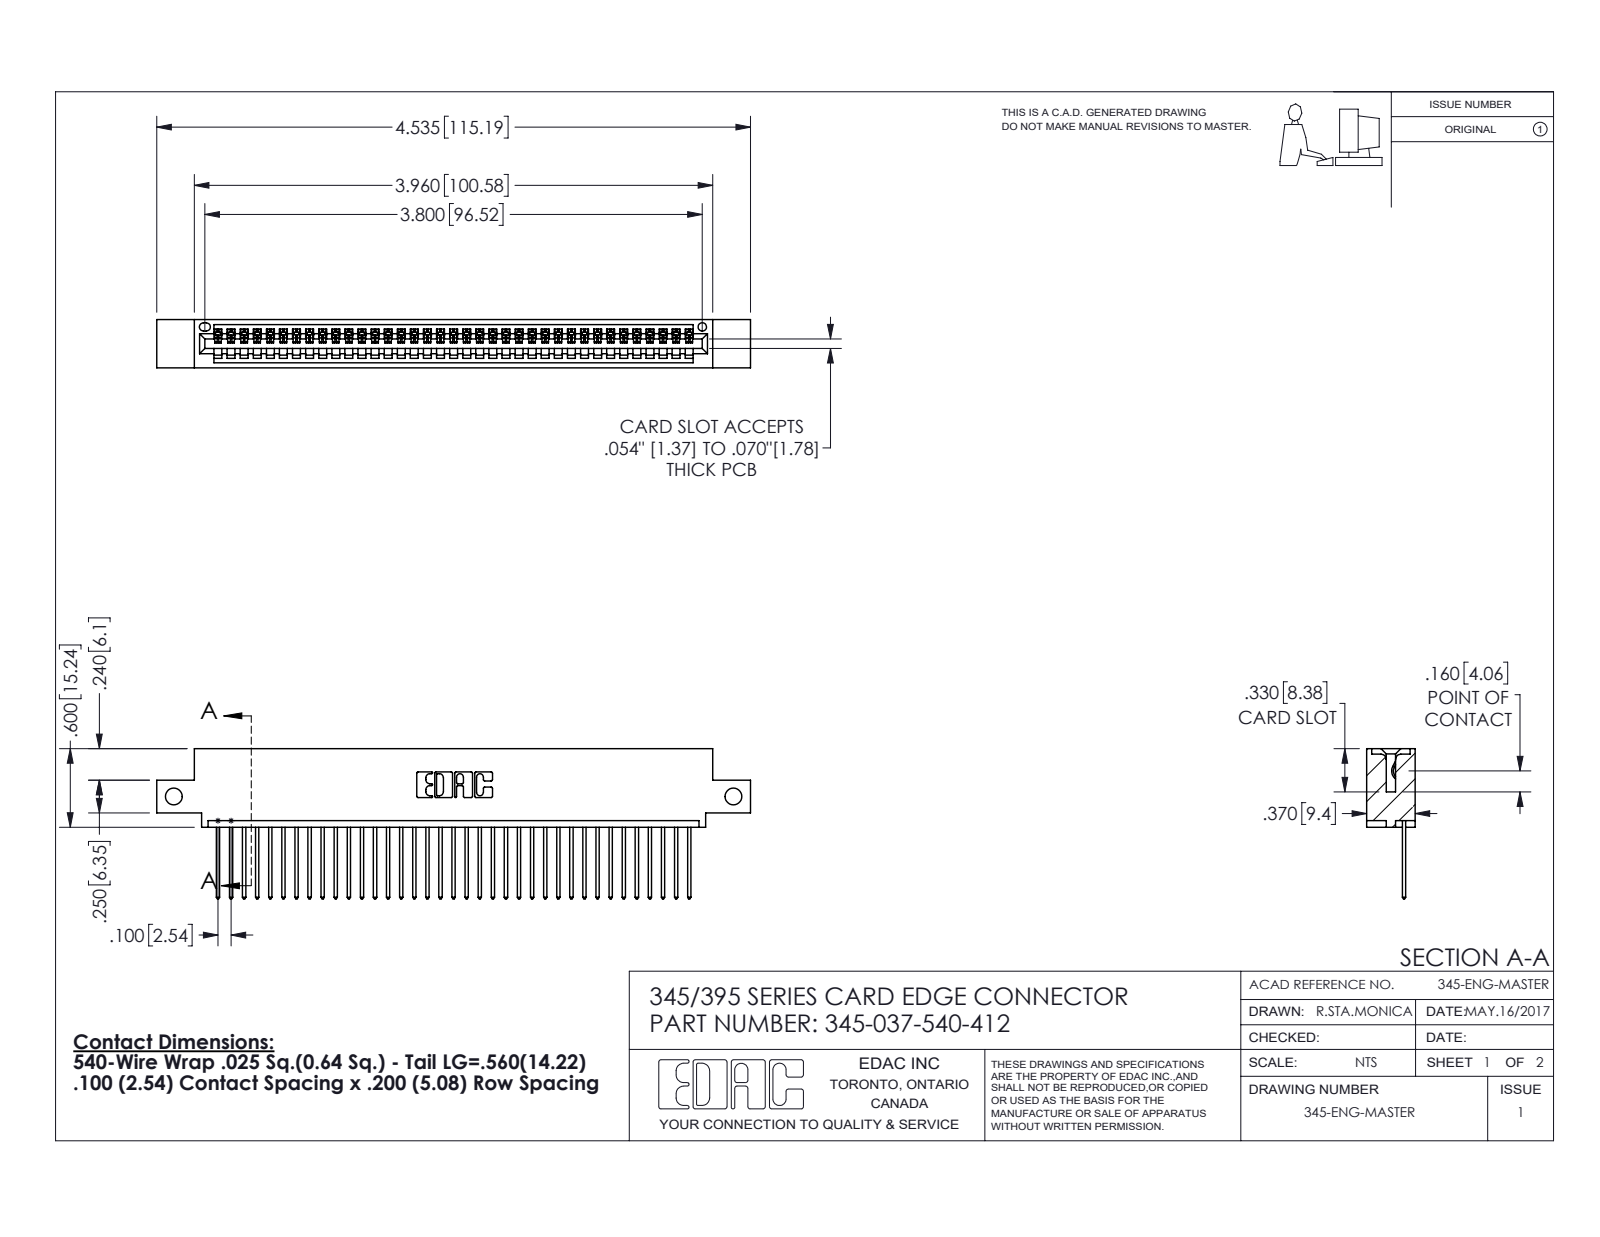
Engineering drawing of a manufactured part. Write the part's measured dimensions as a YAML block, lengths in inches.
part_name: "345-037-540-412; 345 Part_0.110 Offset - Side Mount; 345-292-001_345-293-140"
step_written_by: "SolidWorks 2016 (CONFIG_CONTROL_DESIGN)"
units: inches
bodies: {solids: 38, faces: 2276, planar: 1564, cylindrical: 712, other: 0}
overall_size: [4.535, 1.147, 0.37]
volume: 0.658
surface_area: 22.58
round_holes:
  - {diameter: 0.128, count: 2}
  - {diameter: 0.064, count: 1}
partial_cylinders:
  - {radius: 0.006, count: 74}
  - {radius: 0.01, count: 74}
  - {radius: 0.01, count: 22}
  - {radius: 0.007, count: 6}
  - {radius: 0.031, count: 6}
  - {radius: 0.026, count: 3}
  - {radius: 0.031, count: 2}
  - {radius: 0.04, count: 2}
face_to_face_distances: [0.298, 0.072, 0.37, 0.098, 0.272, 0.025, 0.2, 0.225, 0.149, 0.072]
hole_center_spacings: [4.275]
